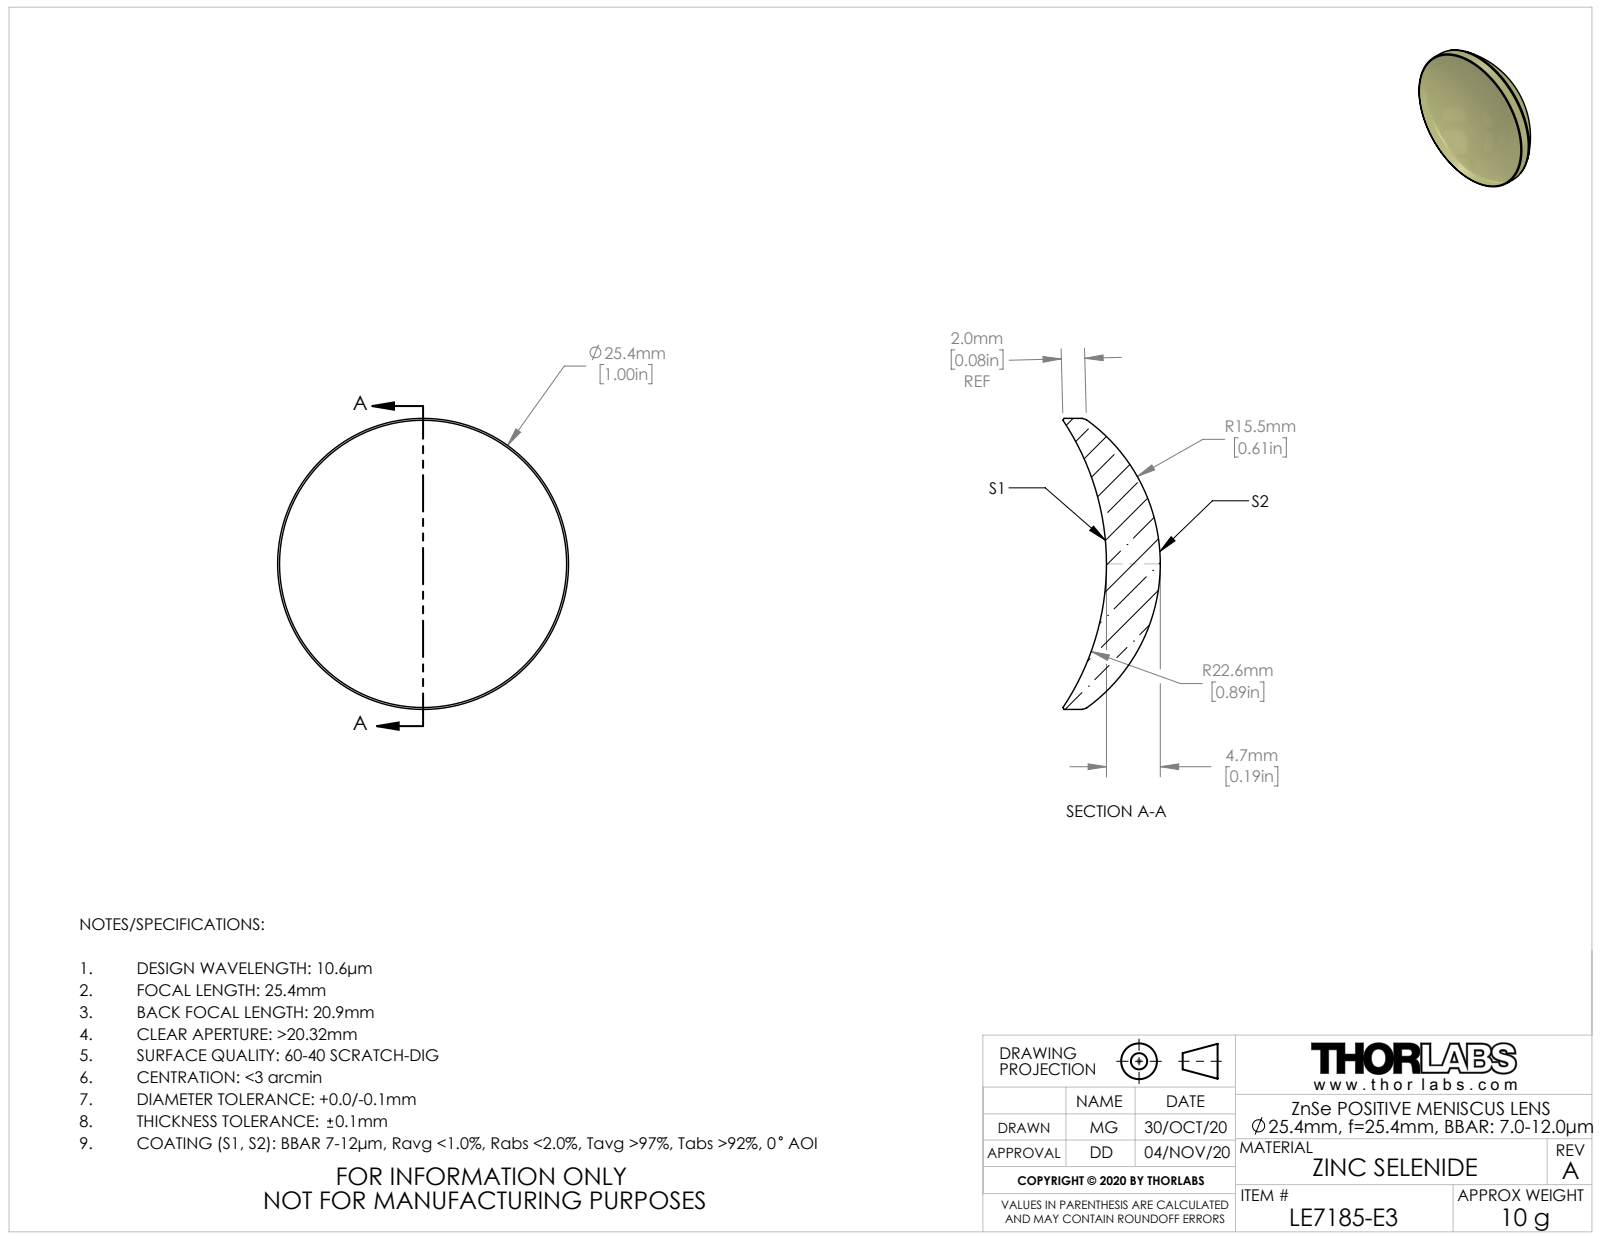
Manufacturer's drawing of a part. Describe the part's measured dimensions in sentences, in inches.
The part is named "TTN225627-E0W". Its 3-D file was written by "SolidWorks 2018 (CONFIG_CONTROL_DESIGN)". It is 1 solid with 10 faces: 0 planar, 2 cylindrical and 8 other. Overall it measures 1 by 1 by 0.335 inches. Its volume is 0.111 cubic inches and its surface area 2.077 square inches. Round bosses or shafts: 1 of diameter 1.
